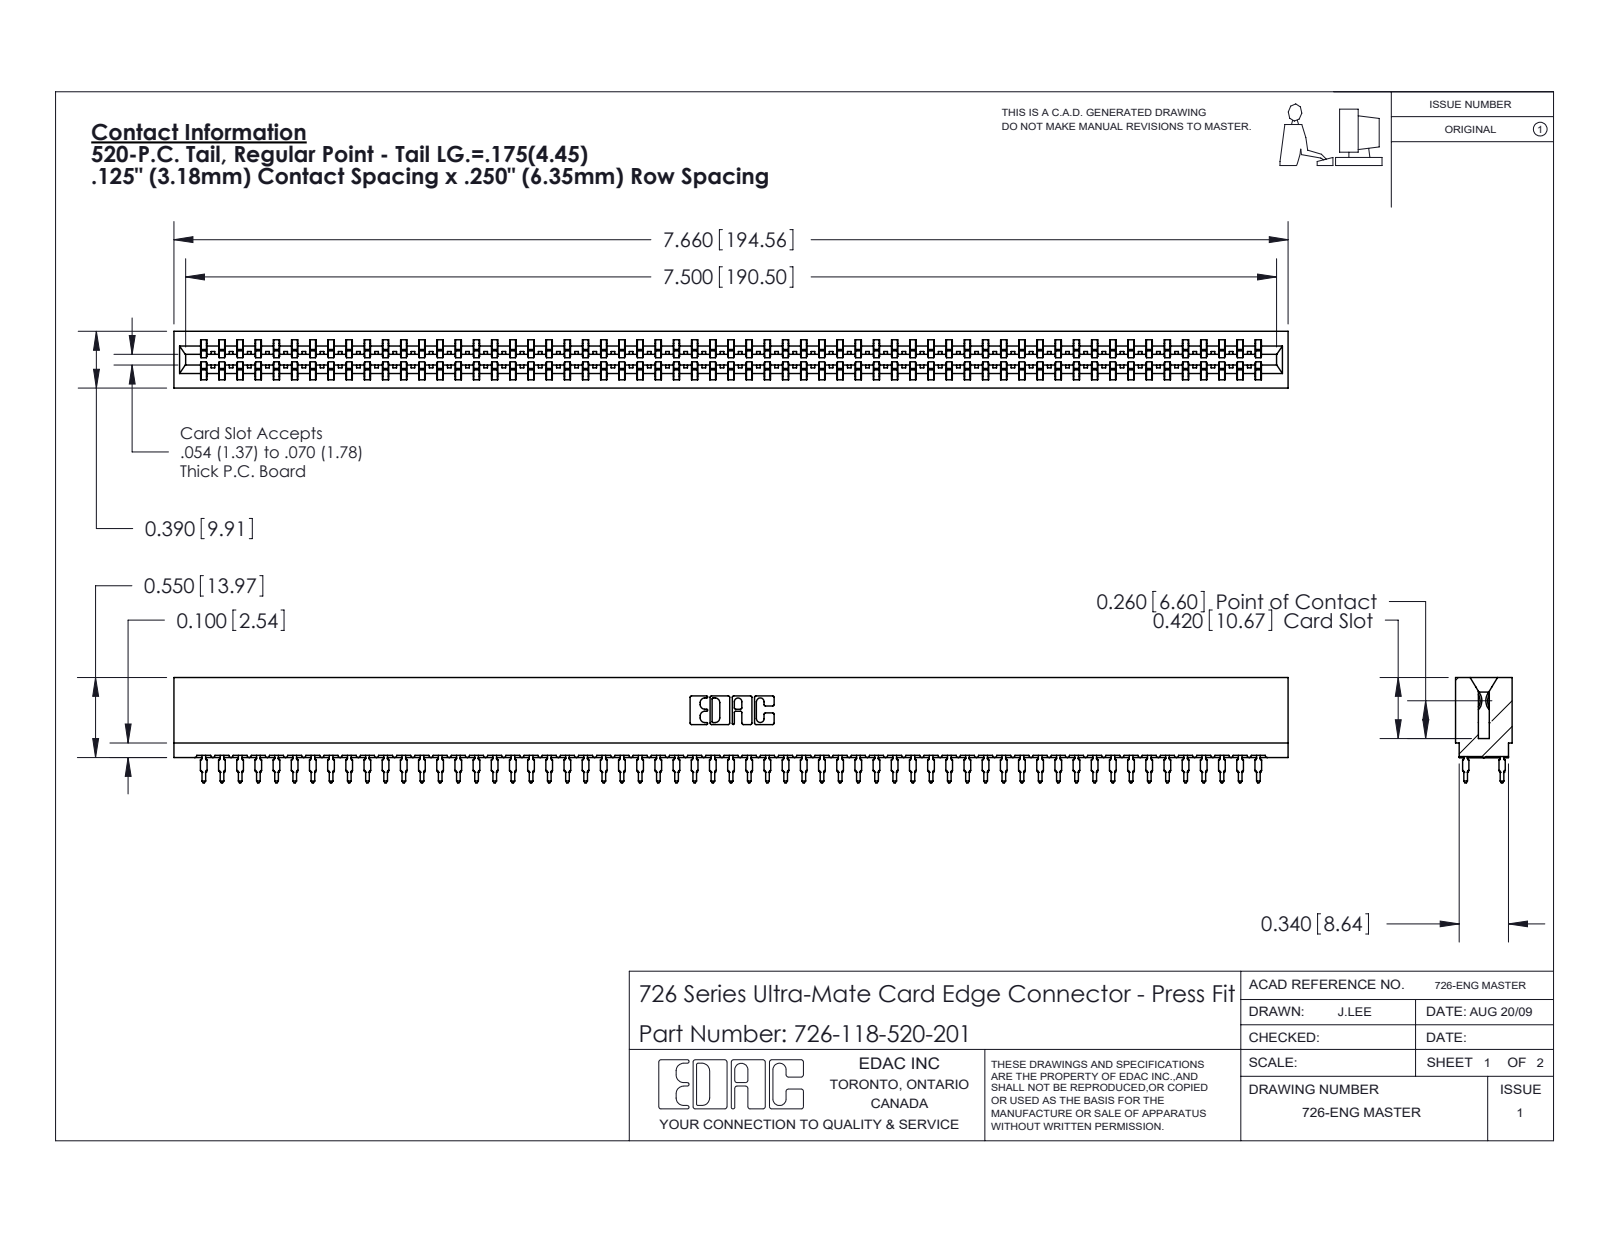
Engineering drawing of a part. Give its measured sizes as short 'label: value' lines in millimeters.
name: 746-292-001_520; 726-118-520-201; 726 Part_.515 Slot Depth - 01
written by: SolidWorks 2020 (CONFIG_CONTROL_DESIGN)
unit: mm
bodies: 119 solids, 10658 faces (5483 planar, 2107 cylindrical, 3068 other)
size: 194.6 × 18.4 × 9.9
volume: 17 710 mm³; area: 29 310 mm²
rounds: 236× R0.5, 60× R0.4, 22× R0.3, 8× R0.1, 8× R0.3, 6× R0.2, 6× R0.8, 3× R0.7
face distances: 1.4, 8.5, 9.9, 0.6, 7.8, 6.4, 7, 2.1, 9.3, 0.8
